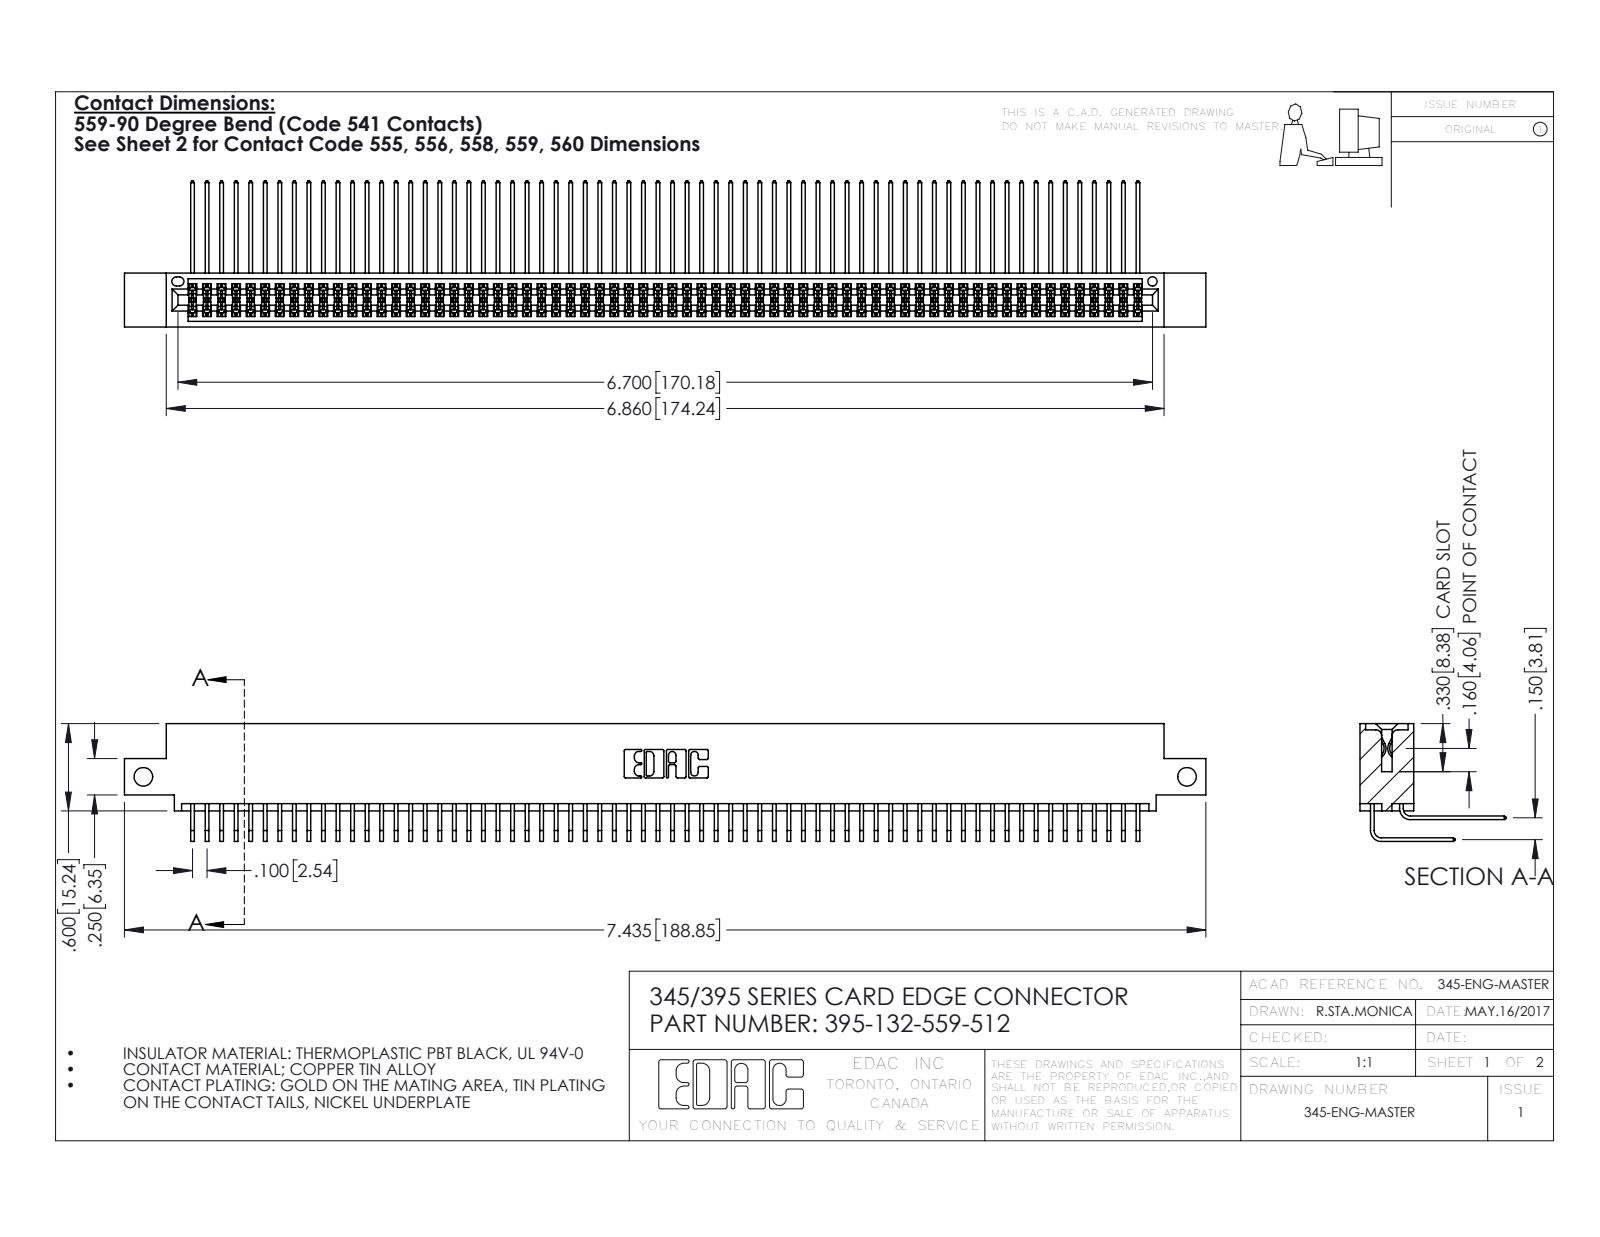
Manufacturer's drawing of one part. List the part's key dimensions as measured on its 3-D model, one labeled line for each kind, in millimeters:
Part name (STEP PRODUCT): 345 Part_0.110 Offset - Side Mount; 345-292-001_558 559 Tail - 1; 345-292-001_559 Tail - 2; 395-132-559-512
STEP written by: SolidWorks 2016 (CONFIG_CONTROL_DESIGN)
Units: millimetres
Bodies: 133 solids, 6994 faces (4704 planar, 2290 cylindrical, 0 other)
Overall size (bounding box): 188.8 × 25.5 × 20.5
Volume: 19 170 mm³ · Surface area: 32 340 mm²
Round holes (diameter × count): ⌀3.3 ×2, ⌀1.6 ×1
Partial cylindrical surfaces — rounded edges, fillets, slot ends (radius × count): R0.2 ×199, R0.3 ×22, R0.2 ×6, R0.8 ×6, R0.7 ×3, R0.4 ×2, R0.5 ×2, R0.6 ×2
Main face-to-face distances: 1.8, 7.6, 5.1, 9.4, 2.5, 6.9, 0.6, 5.7, 4.4, 3.8
Hole centre spacings: 182.2
